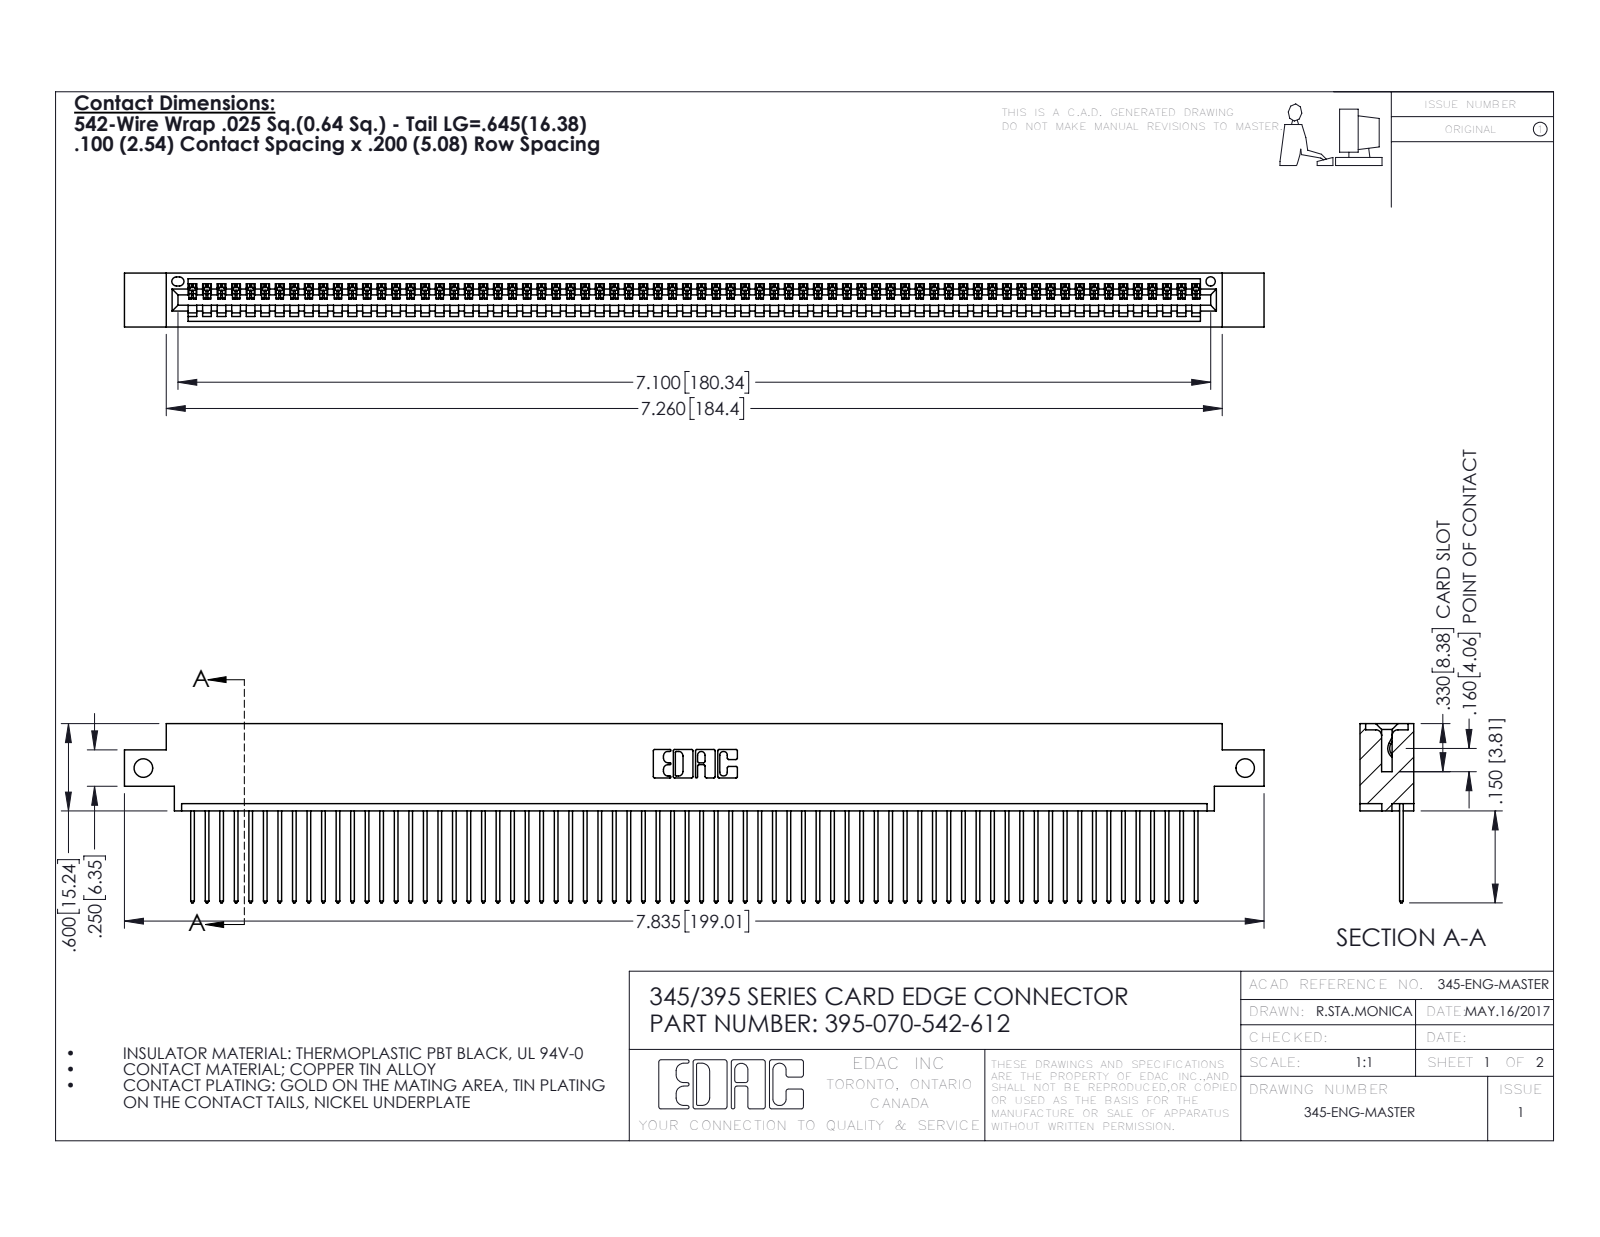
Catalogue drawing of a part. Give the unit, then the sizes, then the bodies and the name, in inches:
Units: inches
Overall size (bounding box): 7.835 × 1.232 × 0.37
Round holes (diameter × count): ⌀0.128 ×2, ⌀0.064 ×1
Partial cylindrical surfaces — rounded edges, fillets, slot ends (radius × count): R0.006 ×140, R0.01 ×140, R0.01 ×22, R0.007 ×6, R0.031 ×6, R0.026 ×3, R0.031 ×2, R0.04 ×2
Main face-to-face distances: 0.072, 0.298, 0.37, 0.098, 0.272, 0.025, 0.2, 0.225, 0.175, 0.149
Hole centre spacings: 7.575
Volume: 1.165 in³ · Surface area: 41.41 in²
Bodies: 71 solids, 4190 faces (2884 planar, 1306 cylindrical, 0 other)
Part name (STEP PRODUCT): 345 Part_0.170 Offset - Side Mount; 345-292-001_345-293-142; 395-070-542-612
STEP written by: SolidWorks 2016 (CONFIG_CONTROL_DESIGN)
